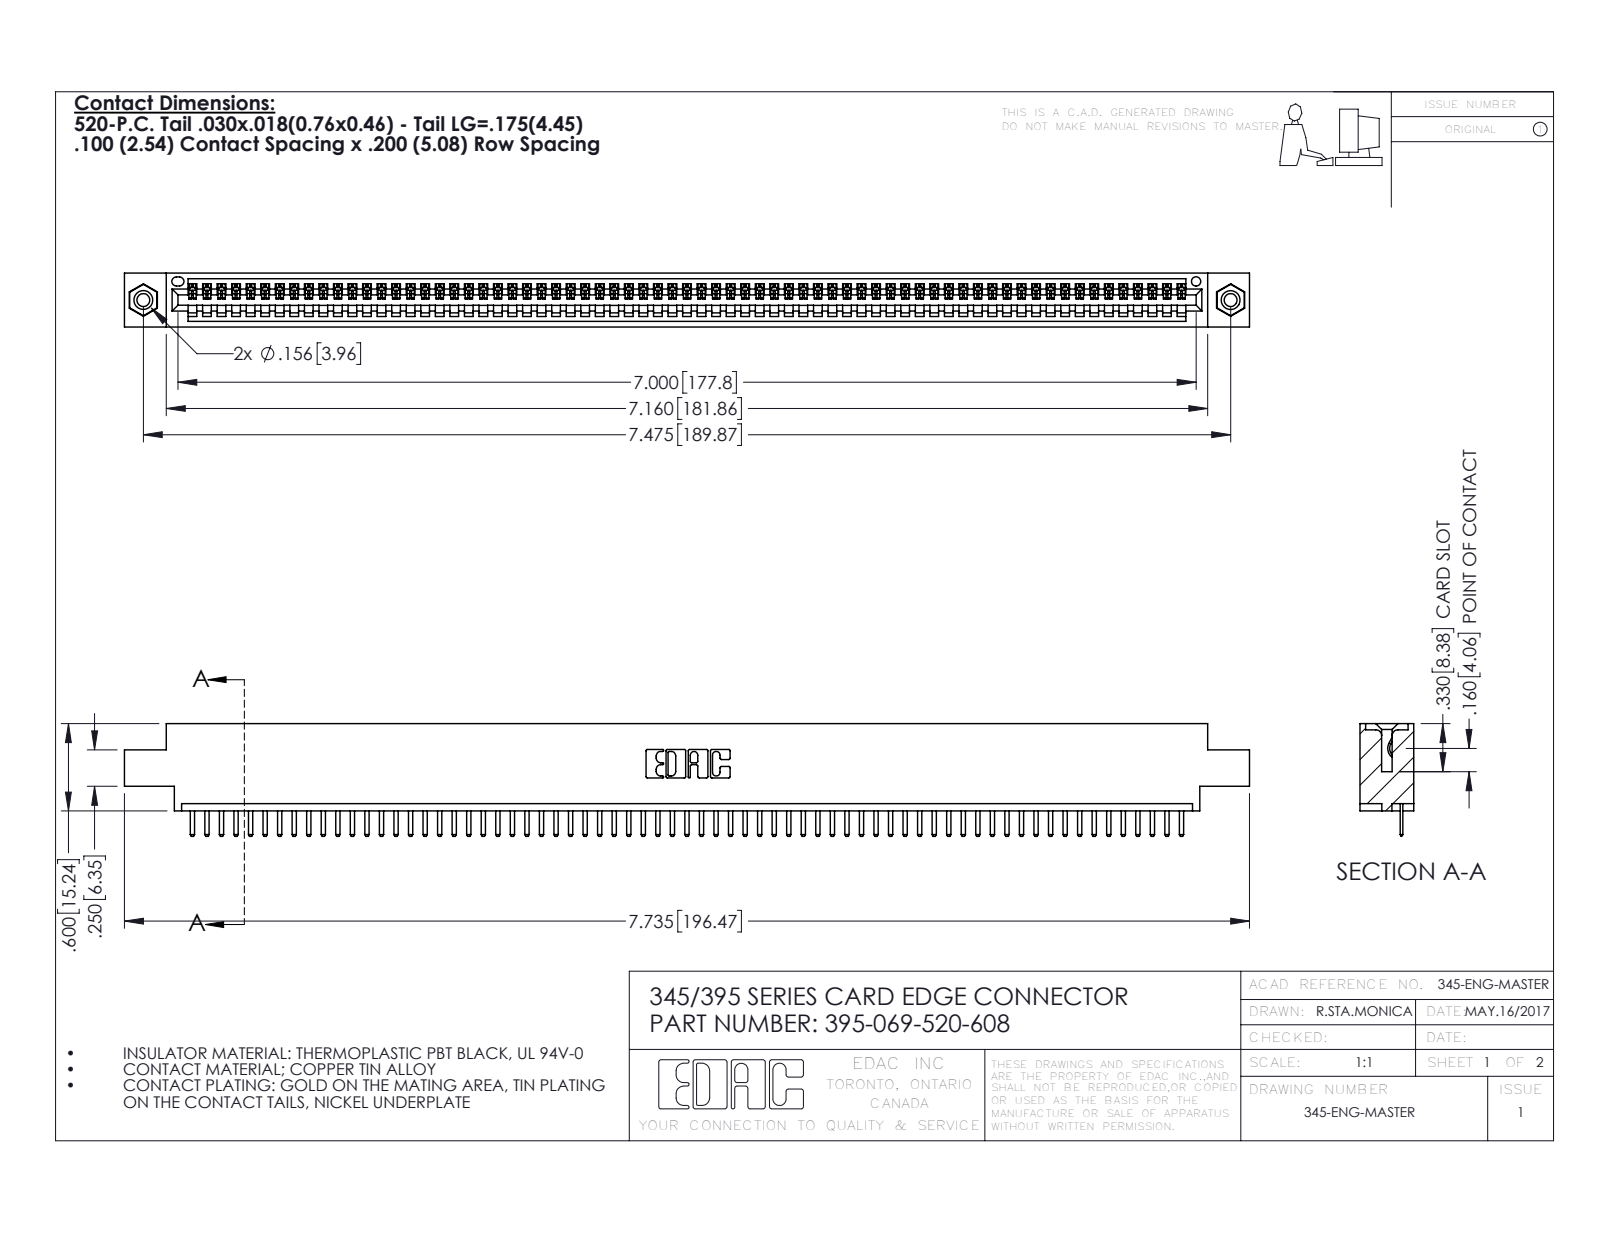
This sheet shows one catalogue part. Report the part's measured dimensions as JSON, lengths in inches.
{"part_name": "345-250-001_345-250-003-102; 345-292-001_345-293-120; 345 Part_0.170 Offset - 0.156 Dia-TI; 395-069-520-608", "step_written_by": "SolidWorks 2016 (CONFIG_CONTROL_DESIGN)", "units": "inches", "bodies": {"solids": 72, "faces": 4468, "planar": 3014, "cylindrical": 1438, "other": 16}, "overall_size": [7.735, 0.775, 0.37], "volume_in3": 1.133, "surface_area_in2": 38.03, "round_holes": [[0.089, 2], [0.125, 2], [0.156, 2], [0.064, 1]], "round_bosses_or_shafts": [[0.155, 2]], "partial_cylinders_radius": [[0.01, 140], [0.006, 138], [0.01, 22], [0.007, 6], [0.031, 6], [0.026, 3], [0.031, 2], [0.04, 2]], "face_to_face_distances": [0.072, 0.298, 0.37, 0.2, 0.098, 0.272, 0.025, 0.225, 0.072, 0.175], "hole_center_spacings": [0.27, 7.239, 7.475]}
